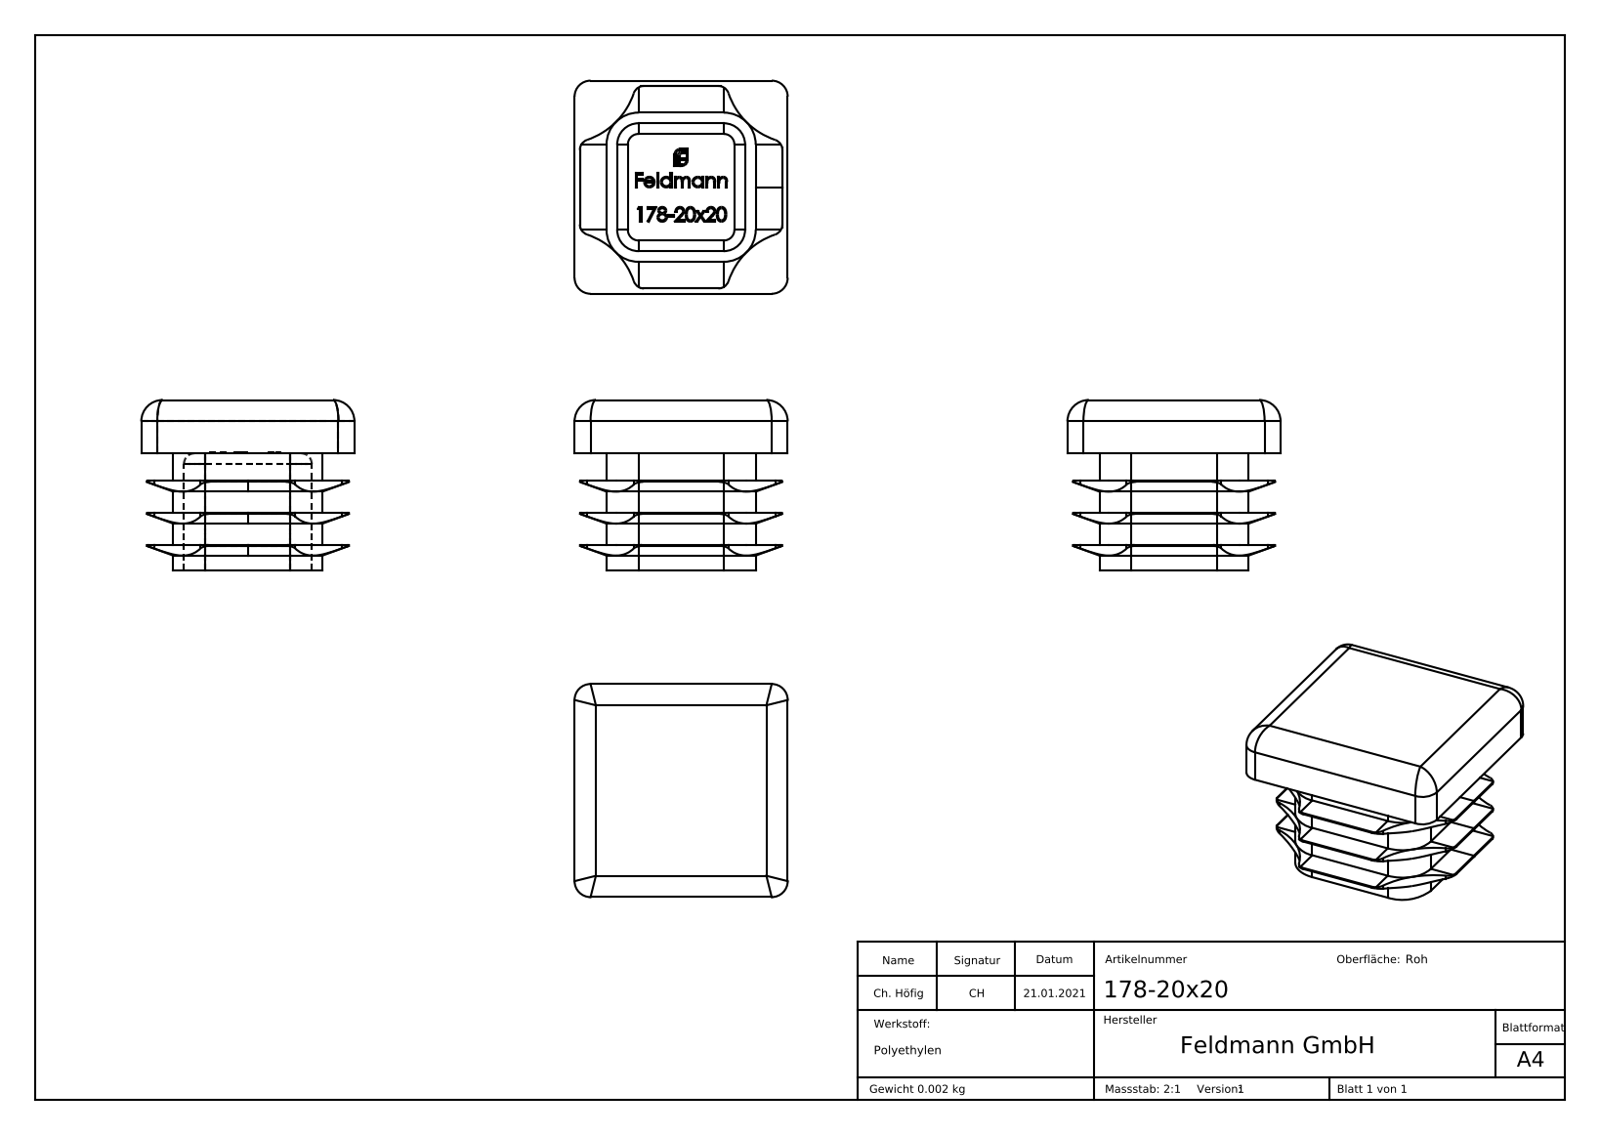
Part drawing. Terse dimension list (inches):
name: 178-20x20
written by: SolidWorks 2018 (CONFIG_CONTROL_DESIGN)
unit: in
bodies: 1 solid, 465 faces (235 planar, 83 cylindrical, 147 other)
size: 0.787 × 0.787 × 0.63
volume: 0.16 in³; area: 4.126 in²
rounds: 12× R0.039, 8× R0.079, 4× R0.059, 4× R0.118, 4× R0.276
face distances: 0.118, 0.197, 0.039, 0.512, 0.63, 0.157, 0.669, 0.472, 0.551, 0.787
